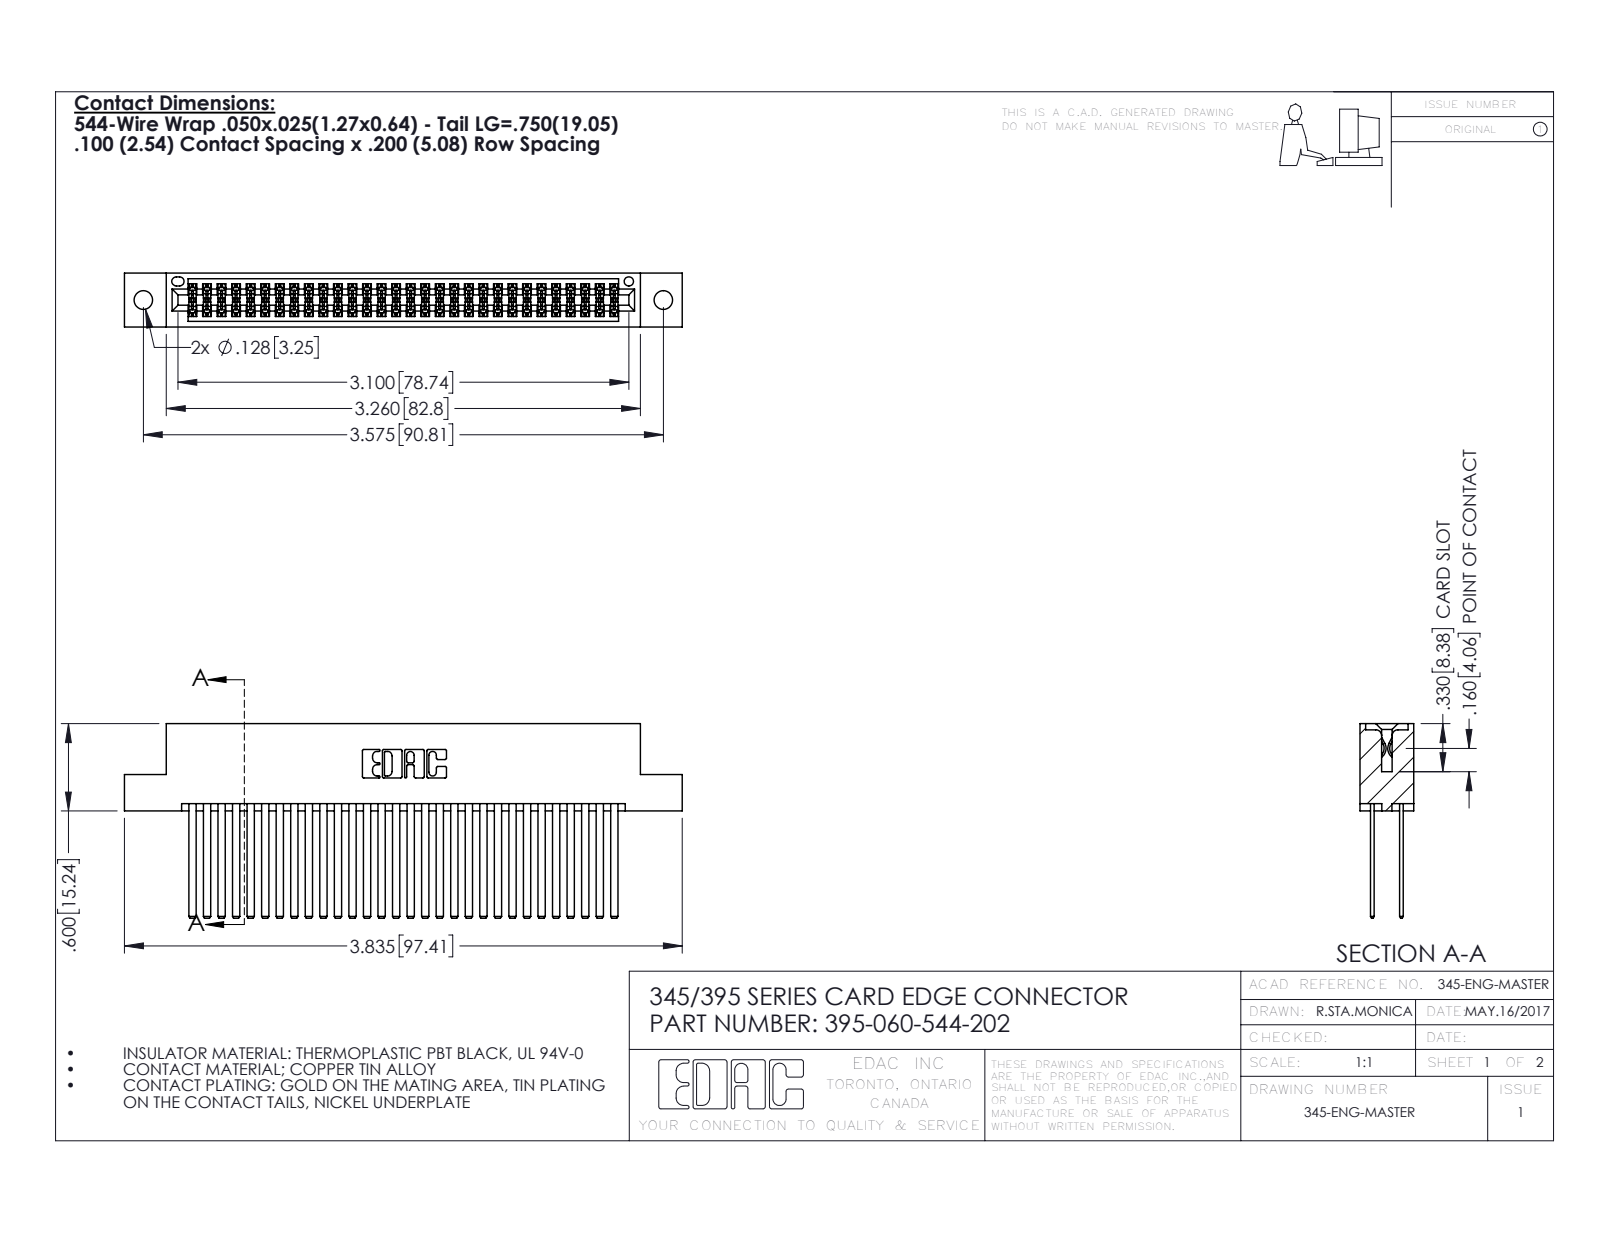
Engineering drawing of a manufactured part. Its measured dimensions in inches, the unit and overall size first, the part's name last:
Units: inches
Overall size (bounding box): 3.835 × 1.337 × 0.37
Round holes (diameter × count): ⌀0.128 ×2, ⌀0.064 ×1
Partial cylindrical surfaces — rounded edges, fillets, slot ends (radius × count): R0.006 ×90, R0.01 ×22, R0.007 ×6, R0.031 ×6, R0.026 ×3, R0.014 ×2, R0.019 ×2, R0.022 ×2
Main face-to-face distances: 0.2, 0.025, 0.298, 0.072, 0.098, 0.272, 0.225, 0.175, 0.37, 0.05
Hole centre spacings: 0.27, 3.34, 3.575
Volume: 0.62 in³ · Surface area: 26.31 in²
Bodies: 61 solids, 2766 faces (1820 planar, 946 cylindrical, 0 other)
Part name (STEP PRODUCT): 345-292-001_345-293-144; 345 Part_Flush Mounting Lugs - 0.128 Dia; 395-060-544-202
STEP written by: SolidWorks 2016 (CONFIG_CONTROL_DESIGN)
